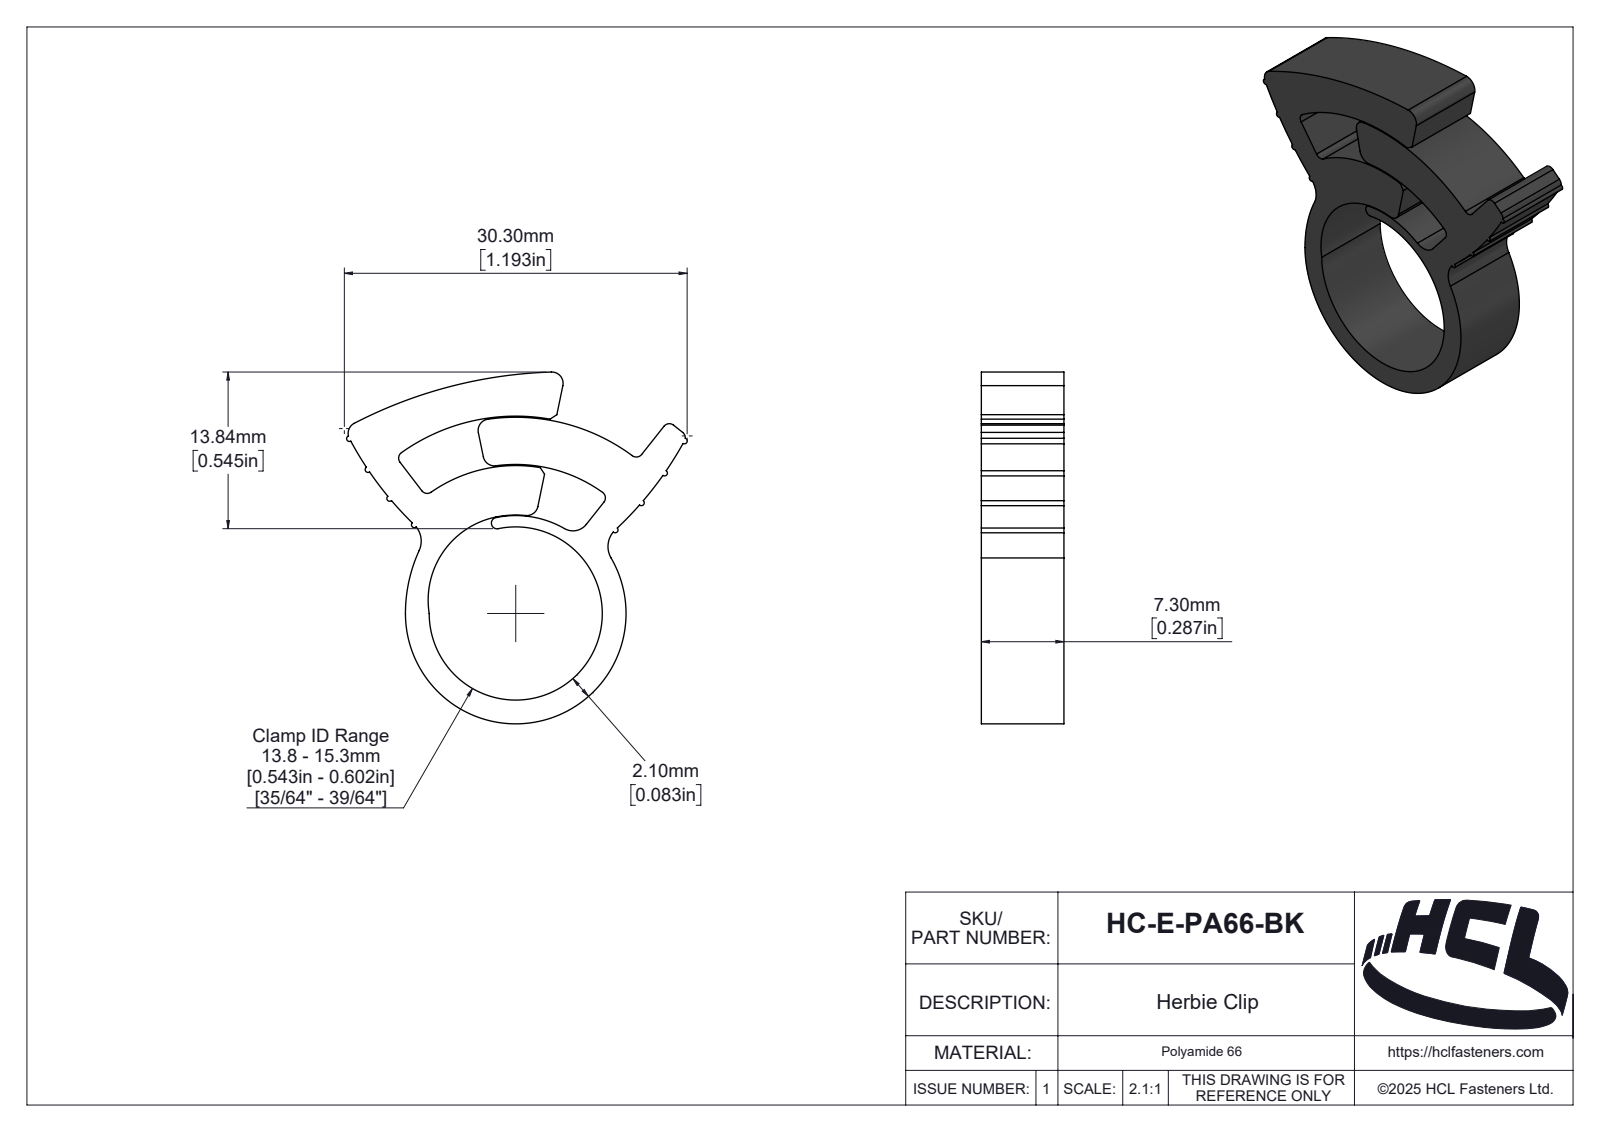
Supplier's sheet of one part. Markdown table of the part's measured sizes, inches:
| quantity | value |
| --- | --- |
| part name | HC-E-PA66-BK |
| STEP written by | SolidWorks 2025 (AUTOMOTIVE_DESIGN) |
| units | inches |
| bodies | 1 solid, 162 faces (13 planar, 100 cylindrical, 49 other) |
| overall size | 1.224 × 1.185 × 0.287 |
| volume | 0.141 in³ |
| surface area | 3.568 in² |
| partial cylindrical surfaces (radius × count) | 0.01 × 8, 0.024 × 6, 0.039 × 5, 0.079 × 2, 0.007 × 1, 0.02 × 1, 0.026 × 1, 0.033 × 1 |
| main face-to-face distances | 0.287 |
